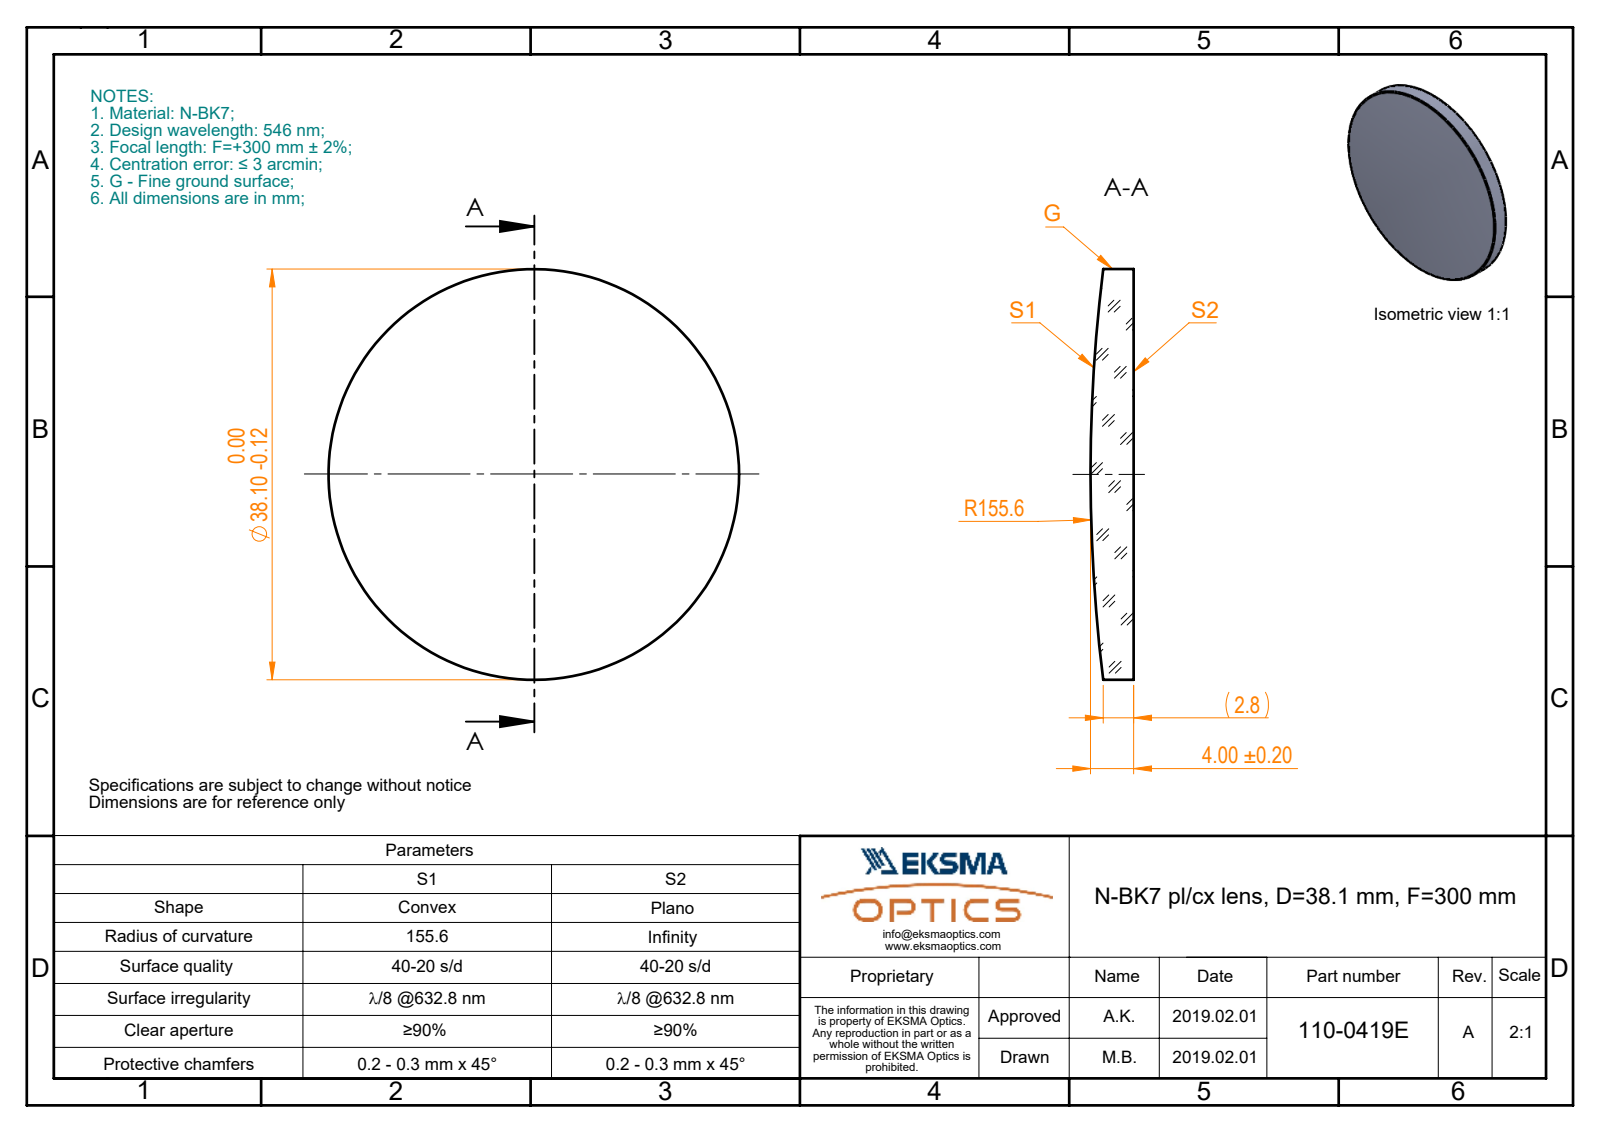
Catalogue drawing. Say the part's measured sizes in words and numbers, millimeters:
The part is named "110-0419E BK7 pl-cx 38.1 F300". Its 3-D file was written by "SolidWorks 2017 (CONFIG_CONTROL_DESIGN)". It is 1 solid with 5 faces: 1 planar, 2 cylindrical and 2 other. Overall it measures 38.1 by 38.1 by 4 millimeters. Its volume is 3 894 cubic millimeters and its surface area 2 623 square millimeters. Round bosses or shafts: 1 of diameter 38.1.
